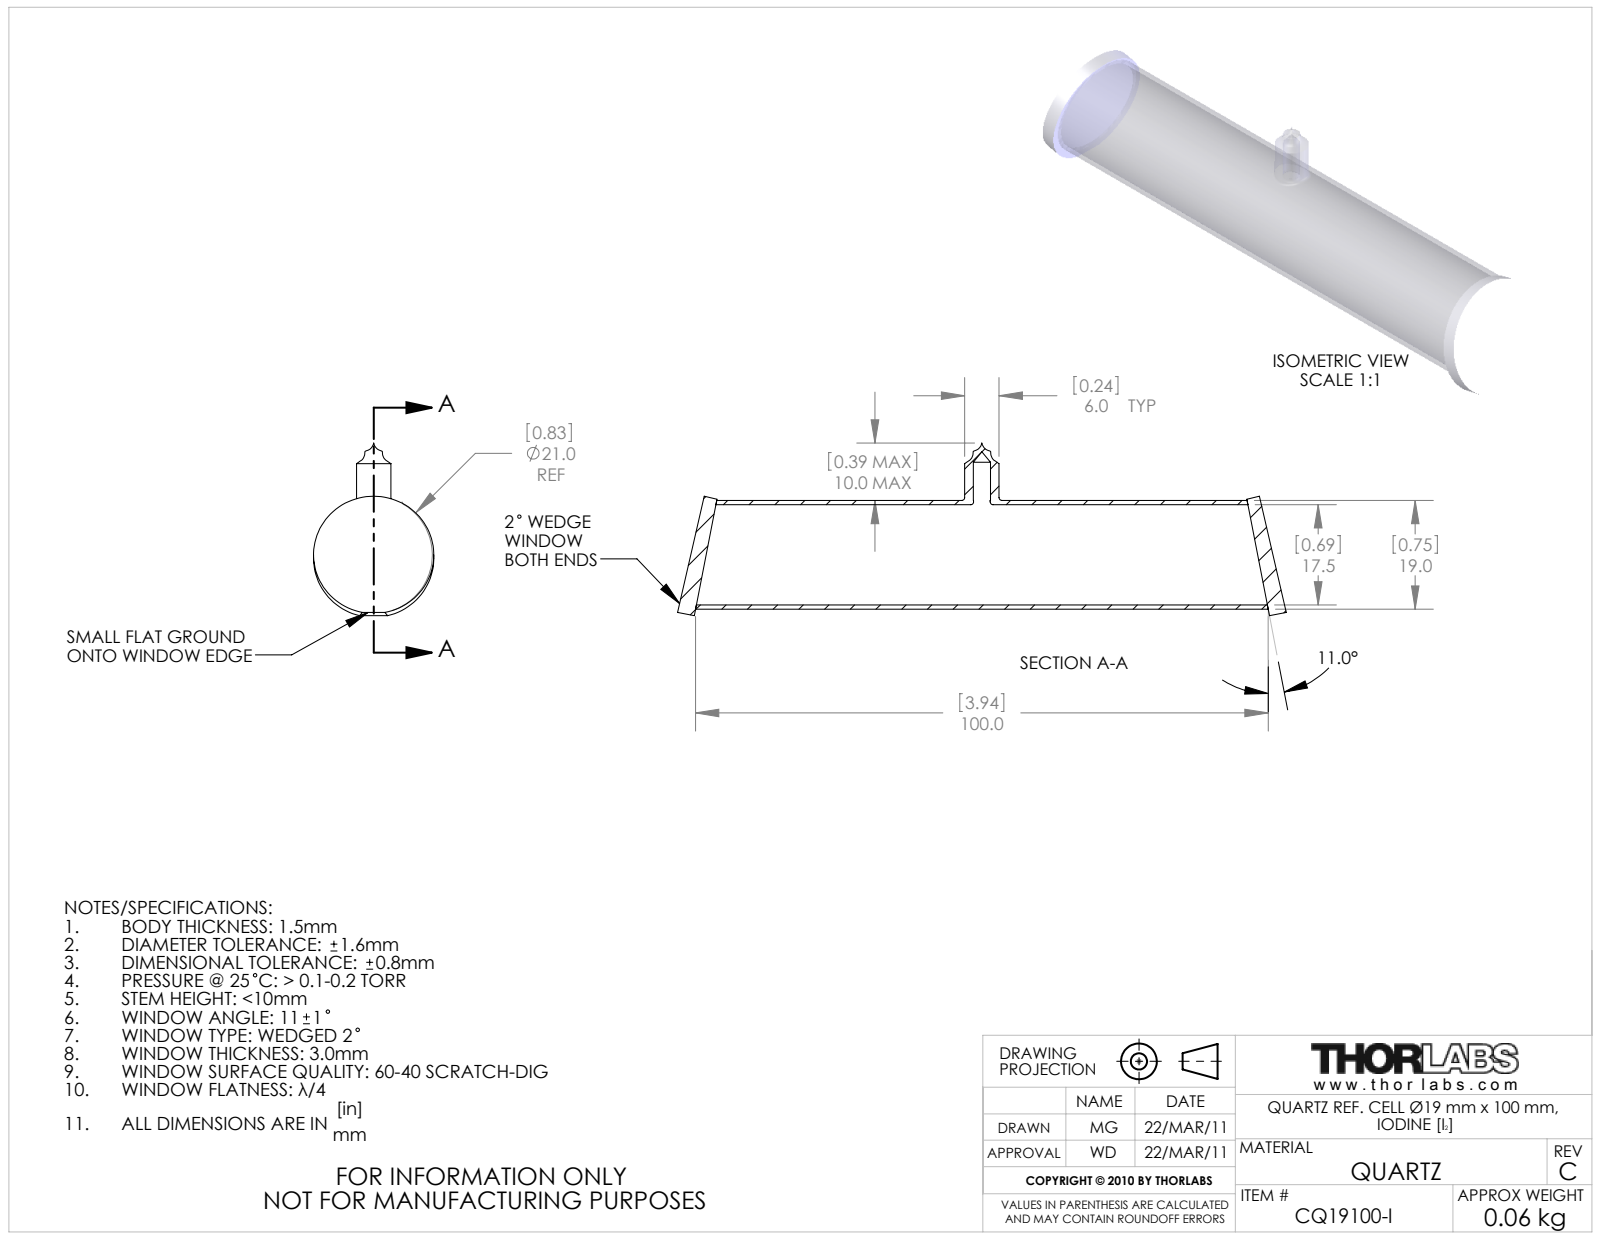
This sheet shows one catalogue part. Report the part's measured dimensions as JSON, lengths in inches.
{"part_name": "12092-E0W", "step_written_by": "SolidWorks 2009 (AUTOMOTIVE_DESIGN)", "units": "inches", "bodies": {"solids": 3, "faces": 33, "planar": 8, "cylindrical": 17, "other": 8}, "overall_size": [4.185, 1.186, 0.827], "volume_in3": 0.373, "surface_area_in2": 20.26, "round_holes": [[0.115, 1], [0.118, 1], [0.689, 1]], "round_bosses_or_shafts": [[0.827, 2], [0.748, 1], [0.236, 1]]}
